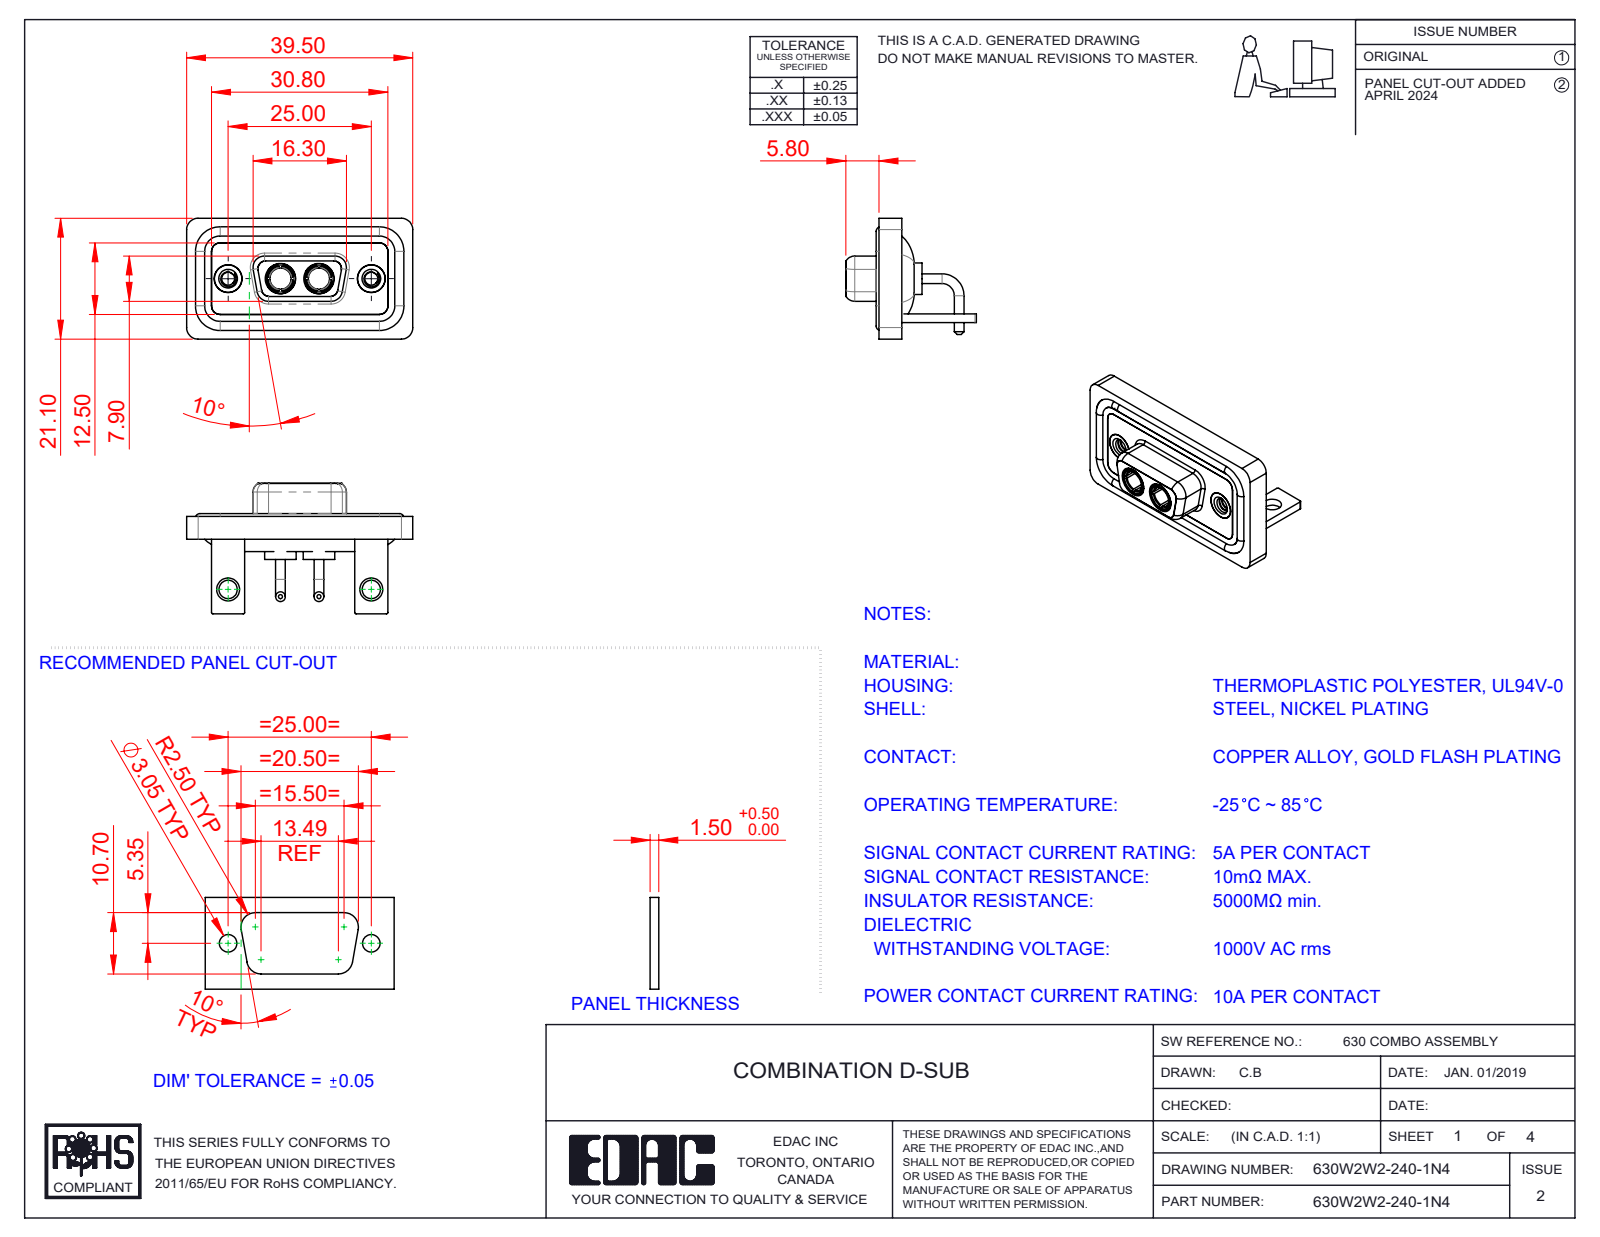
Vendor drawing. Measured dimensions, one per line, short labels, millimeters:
name: 630Combo Waterproof Housing_09 Contacts; 630Combo Shell Front_09 Contacts; 630Combo Stabilizer Bracket_50 Contacts; 630Combo Shell Rear_09 Contacts (+4 more)
written by: SolidWorks 2023 (CONFIG_CONTROL_DESIGN)
unit: mm
bodies: 13 solids, 590 faces (183 planar, 262 cylindrical, 145 other)
size: 39.5 × 22.8 × 21.1
volume: 5 067 mm³; area: 8 420 mm²
holes: 4× ⌀4.85, 2× ⌀2.26, 2× ⌀3.2, 2× ⌀3.7, 2× ⌀4, 2× ⌀4.05, 2× ⌀5, 2× ⌀5.3
bosses: 4× ⌀1.7, 4× ⌀1.6, 2× ⌀5.5, 2× ⌀5.2, 2× ⌀4.96, 2× ⌀4.95, 2× ⌀4.8, 2× ⌀4.75
rounds: 19× R2, 18× R1.5, 16× R0.25, 8× R1.35, 8× R1.6, 5× R0.5, 4× R0.6, 4× R0.65
face distances: 0.4, 2.9, 1.5, 1.8, 1.1, 3.7, 0.8, 2.5, 1.6, 3.1
hole spacings: 9.14, 15.86, 25, 6.72
